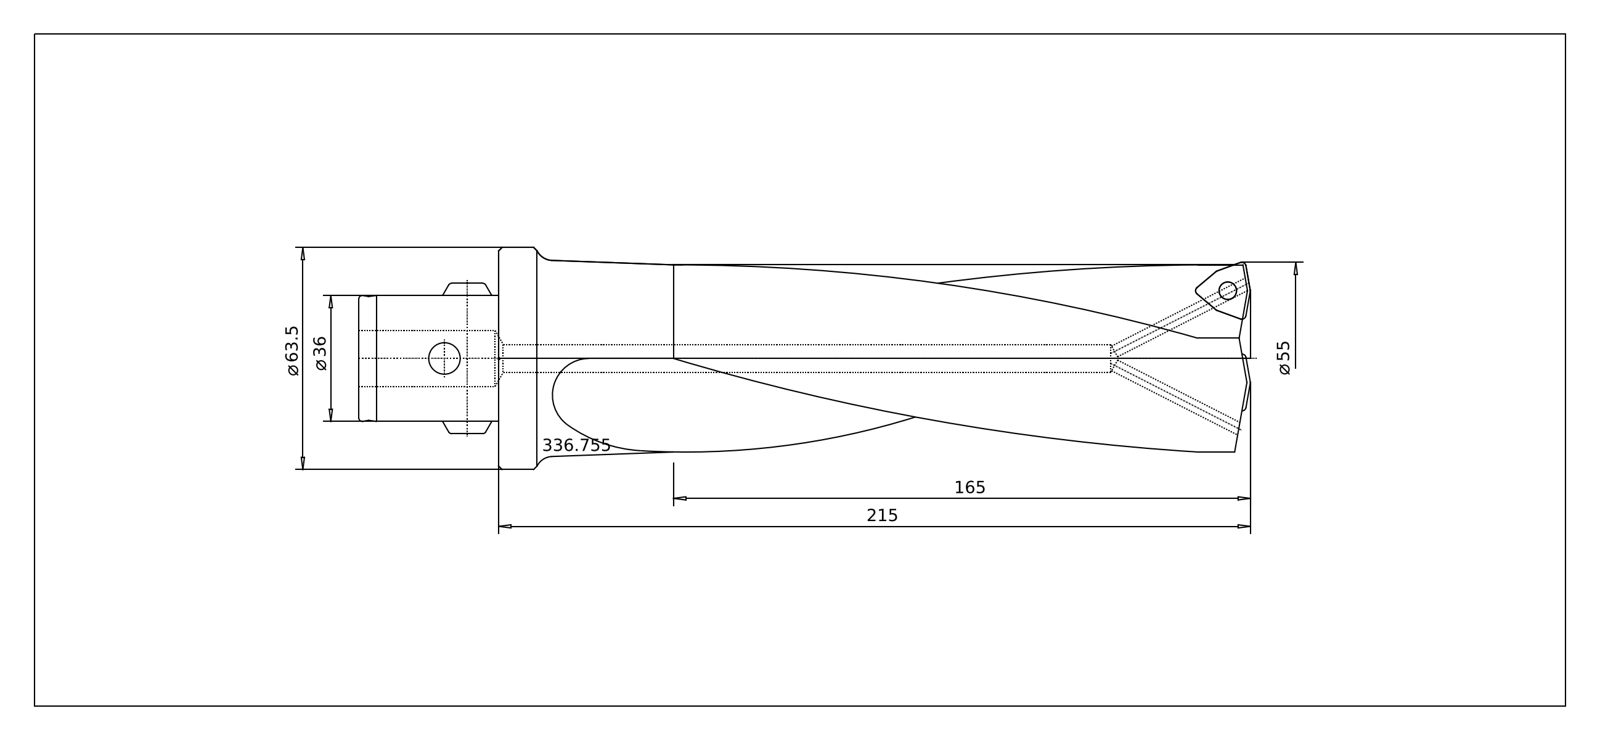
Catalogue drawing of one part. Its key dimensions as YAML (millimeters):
part_name: "336.755 Kaiser WB 55-165 X CK6|694.143 Kaiser ETL M4 X 11,8 T15 IP 10S_Standard;NONE; 336.755 Kaiser WB 55-165 X CK6|336.755 Kaiser WB 55-165 X CK6_Standard-2;NONE; 336.755 Kaiser WB 55-165 X CK6|336.755 Kaiser WB 55-165 X CK6_Standard-1;NONE; 336.755 Kaiser WB 55-165 X CK6|336.755 Kaiser WB 55-165 X CK6_Standard;NONE (+2 more)"
step_written_by: "ACIS (automotive_design)"
units: millimeters
bodies: {solids: 7, faces: 371, planar: 83, cylindrical: 110, other: 178}
overall_size: [255, 63.5, 63.5]
volume: 350069
surface_area: 59553
round_holes:
  - {diameter: 3.1, count: 2}
  - {diameter: 3.35, count: 2}
  - {diameter: 4, count: 2}
  - {diameter: 4.4, count: 2}
  - {diameter: 5, count: 1}
  - {diameter: 9, count: 1}
  - {diameter: 14, count: 1}
  - {diameter: 16, count: 1}
  - {diameter: 18.5, count: 1}
round_bosses_or_shafts:
  - {diameter: 5.5, count: 2}
  - {diameter: 63.5, count: 1}
  - {diameter: 53.48, count: 1}
  - {diameter: 36, count: 1}
  - {diameter: 13.93, count: 1}
  - {diameter: 10, count: 1}
partial_cylinders:
  - {radius: 0.25, count: 12}
  - {radius: 0.6, count: 12}
  - {radius: 0.1, count: 5}
  - {radius: 2.1, count: 4}
  - {radius: 1, count: 1}
  - {radius: 1.82, count: 1}
face_to_face_distances: [40, 4.54, 4.76, 5.06, 9.82, 12, 52, 4.5, 5.32, 0.56]
hole_center_spacings: [26.12, 223.9, 224.15, 224.64, 224.88]
